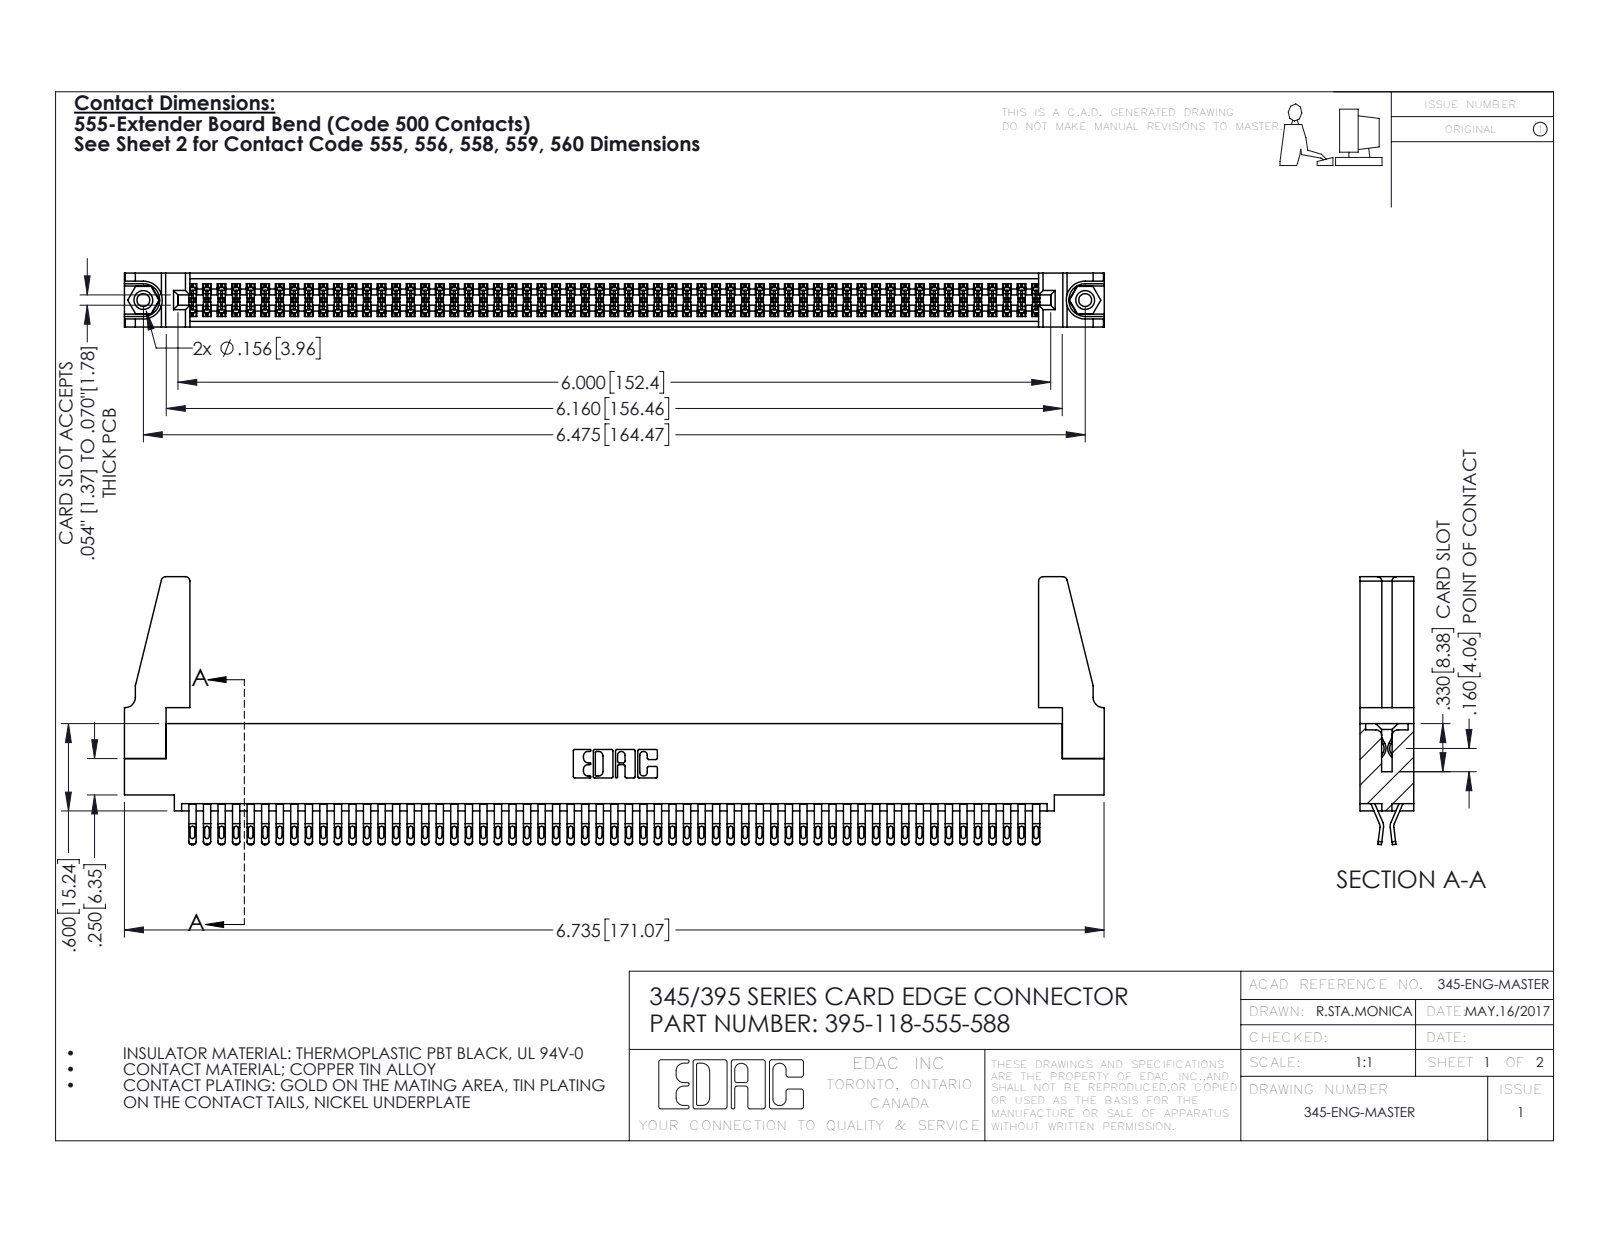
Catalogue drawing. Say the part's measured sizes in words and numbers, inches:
The part is named "345-220-078_345-220-088; 395-118-555-588; 345-250-001_345-250-001-102; 345-292-001_555 Tail (+1 more)". Its 3-D file was written by "SolidWorks 2016 (CONFIG_CONTROL_DESIGN)". It is 123 solids with 6862 faces: 3814 planar, 3032 cylindrical and 16 other. Overall it measures 6.736 by 1.842 by 0.37 inches. Its volume is 1.239 cubic inches and its surface area 46.4 square inches. Round holes: 2 of diameter 0.089, 2 of diameter 0.125, 2 of diameter 0.156, 1 of diameter 0.064. Round bosses or shafts: 2 of diameter 0.155. Partial cylindrical surfaces (rounded edges, fillets, slot ends): 295 of radius 0.016, 236 of radius 0.02, 177 of radius 0.006, 22 of radius 0.01, 8 of radius 0.03, 6 of radius 0.007, 6 of radius 0.031, 3 of radius 0.026. The main face-to-face distances are 0.072, 0.298, 0.37, 0.025, 0.2, 0.098, 0.272, 0.225, 0.175, 0.149. The hole center spacings are 0.27, 6.239, 6.475.
